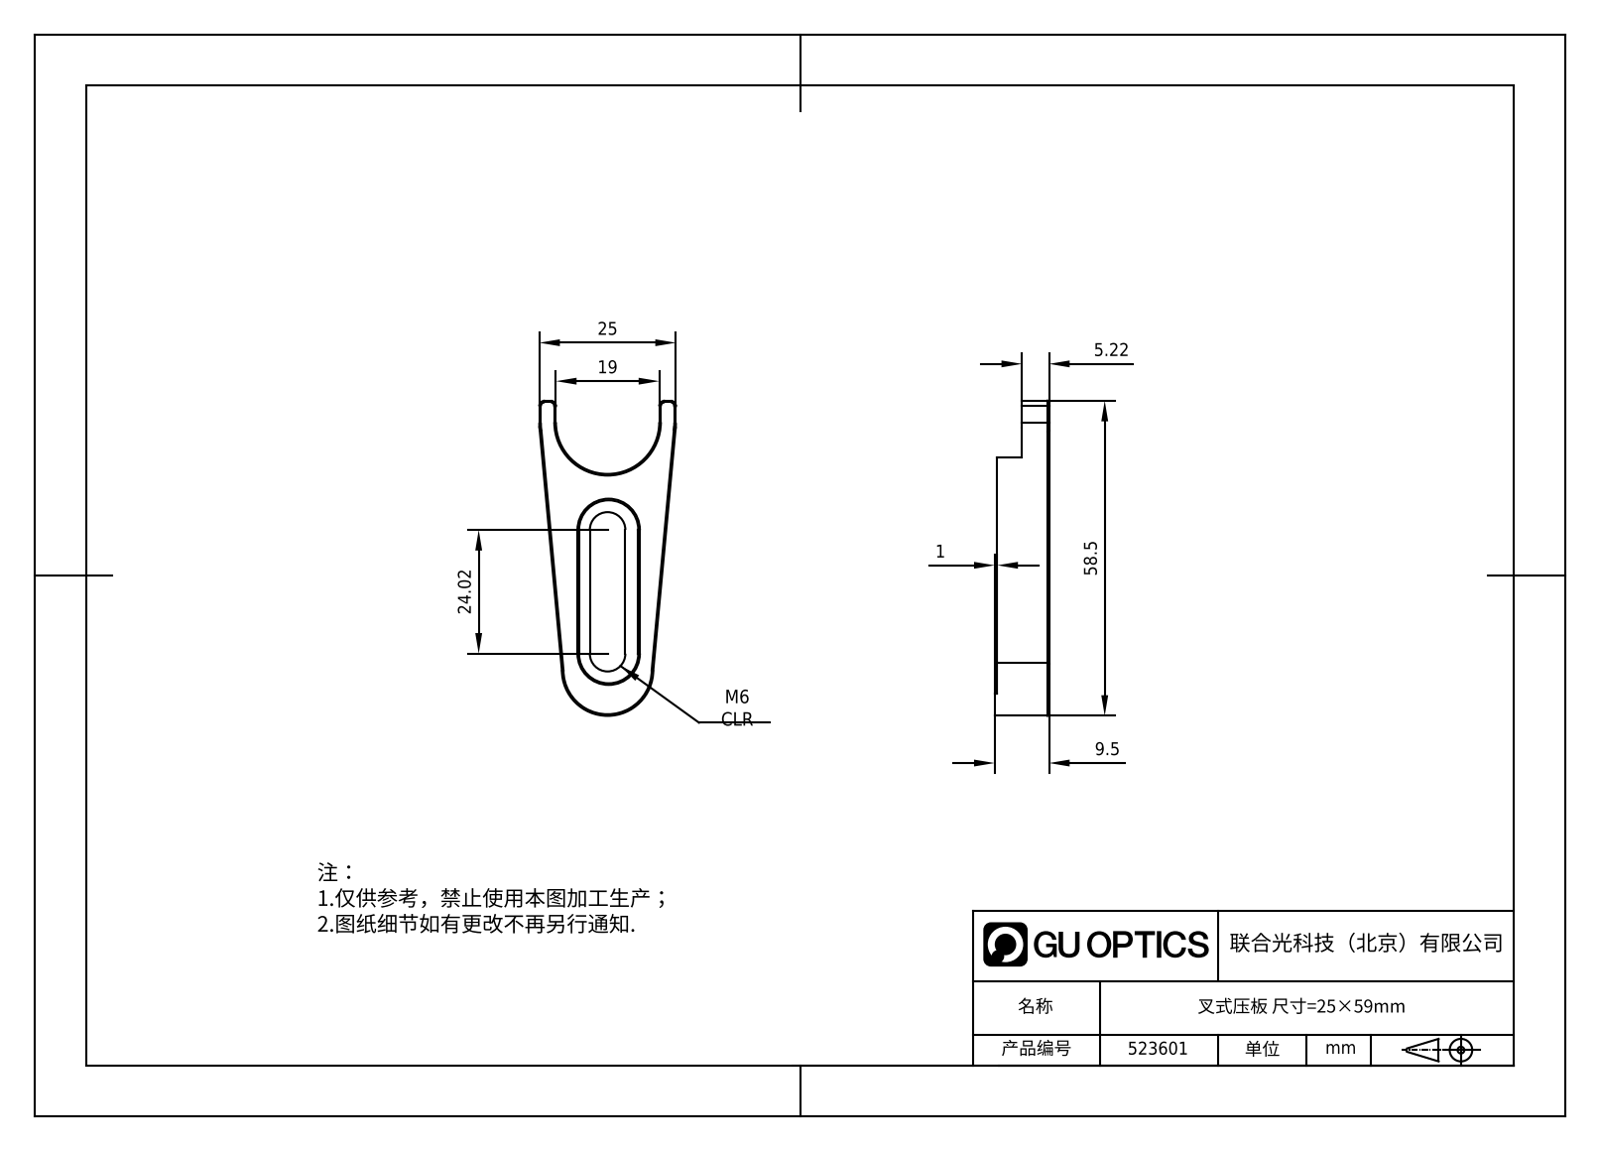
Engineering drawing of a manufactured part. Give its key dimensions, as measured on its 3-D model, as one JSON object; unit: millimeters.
{"part_name": "523601", "step_written_by": "SolidWorks 2020 (CONFIG_CONTROL_DESIGN)", "units": "millimeters", "bodies": {"solids": 1, "faces": 53, "planar": 26, "cylindrical": 15, "other": 12}, "overall_size": [58.55, 25.4, 9.5], "volume_mm3": 4896, "surface_area_mm2": 3345, "partial_cylinders_radius": [[1, 4], [3.3, 2], [5.5, 2], [10, 2], [200, 2], [8.5, 1], [9.6, 1], [13, 1]], "face_to_face_distances": [8.5, 4.5, 1, 4, 3.5, 5, 6.6, 8.6, 2, 2.4]}
